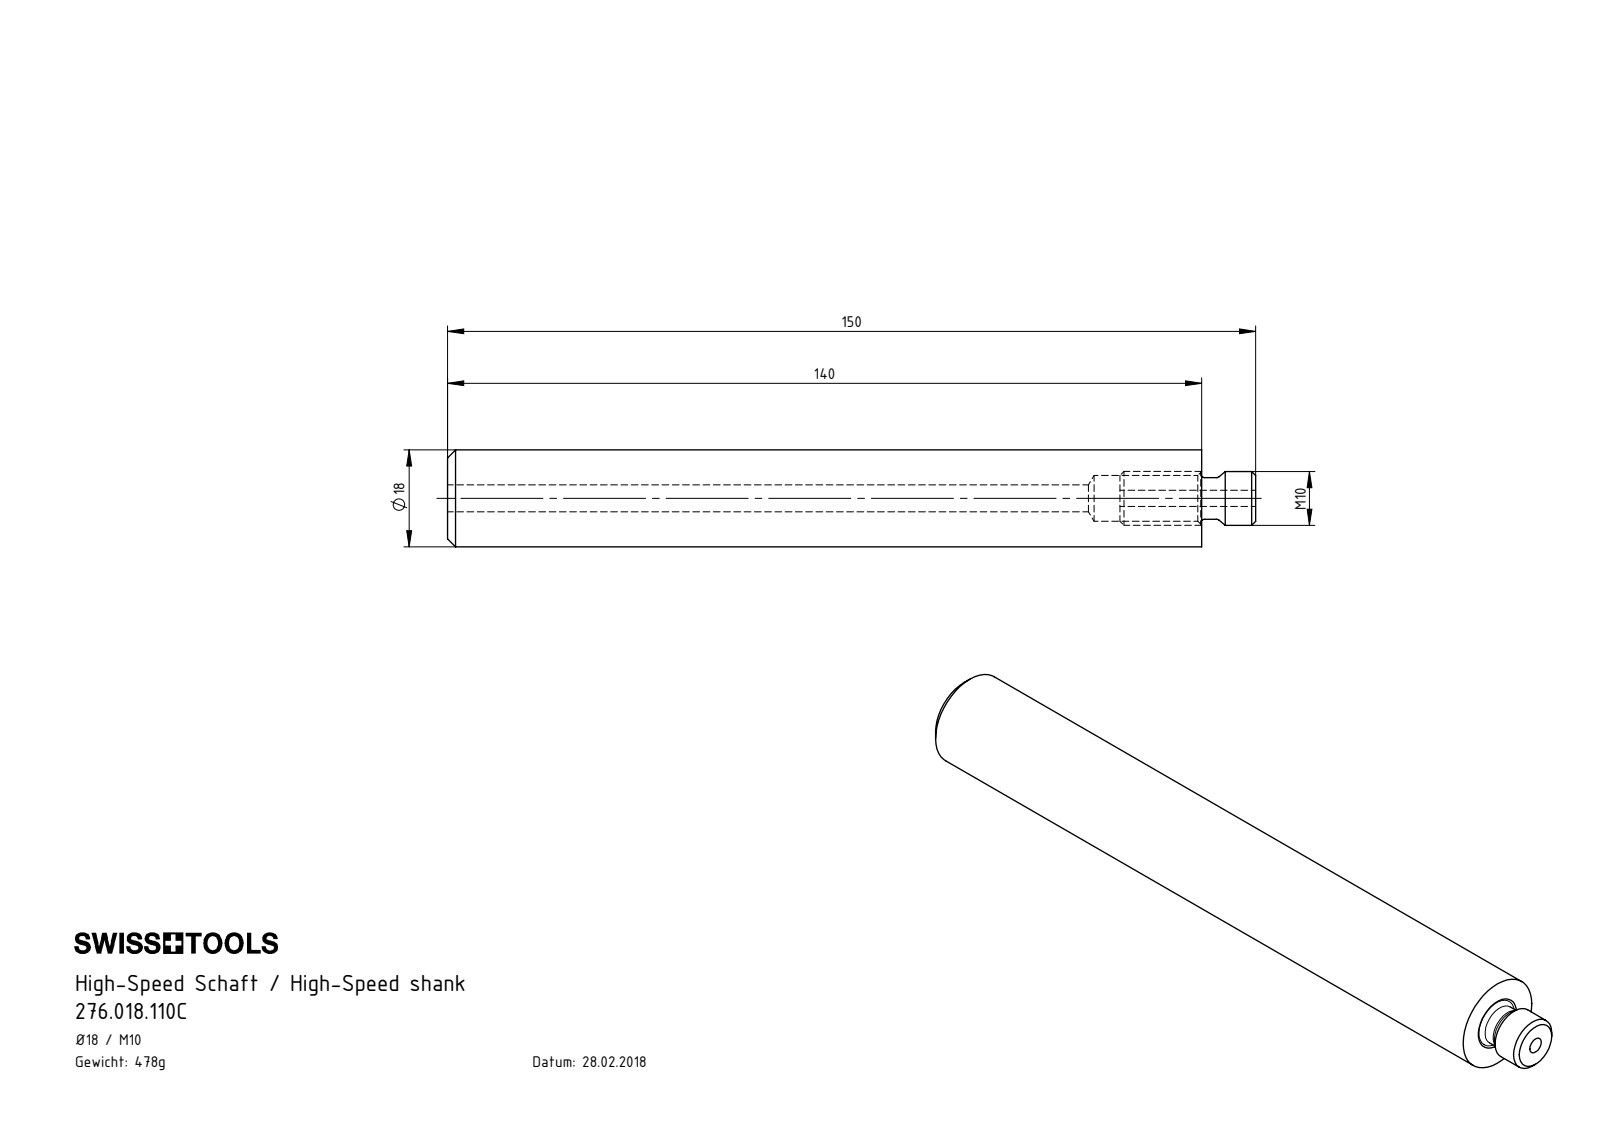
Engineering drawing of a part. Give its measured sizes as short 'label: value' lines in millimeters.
name: HM1-U18.001.140_A; 276.018.110C; HM1-BG1.010.025_A
written by: SolidWorks 2017 (CONFIG_CONTROL_DESIGN)
unit: mm
bodies: 2 solids, 35 faces (5 planar, 14 cylindrical, 16 other)
size: 150 × 18 × 18
volume: 33 712 mm³; area: 11 882 mm²
holes: 1× ⌀3, 1× ⌀5, 1× ⌀8.5
bosses: 1× ⌀18, 1× ⌀10, 1× ⌀7.7
face distances: 140, 150, 10, 124.8, 15.2, 25.2, 139.8, 15, 10.2
